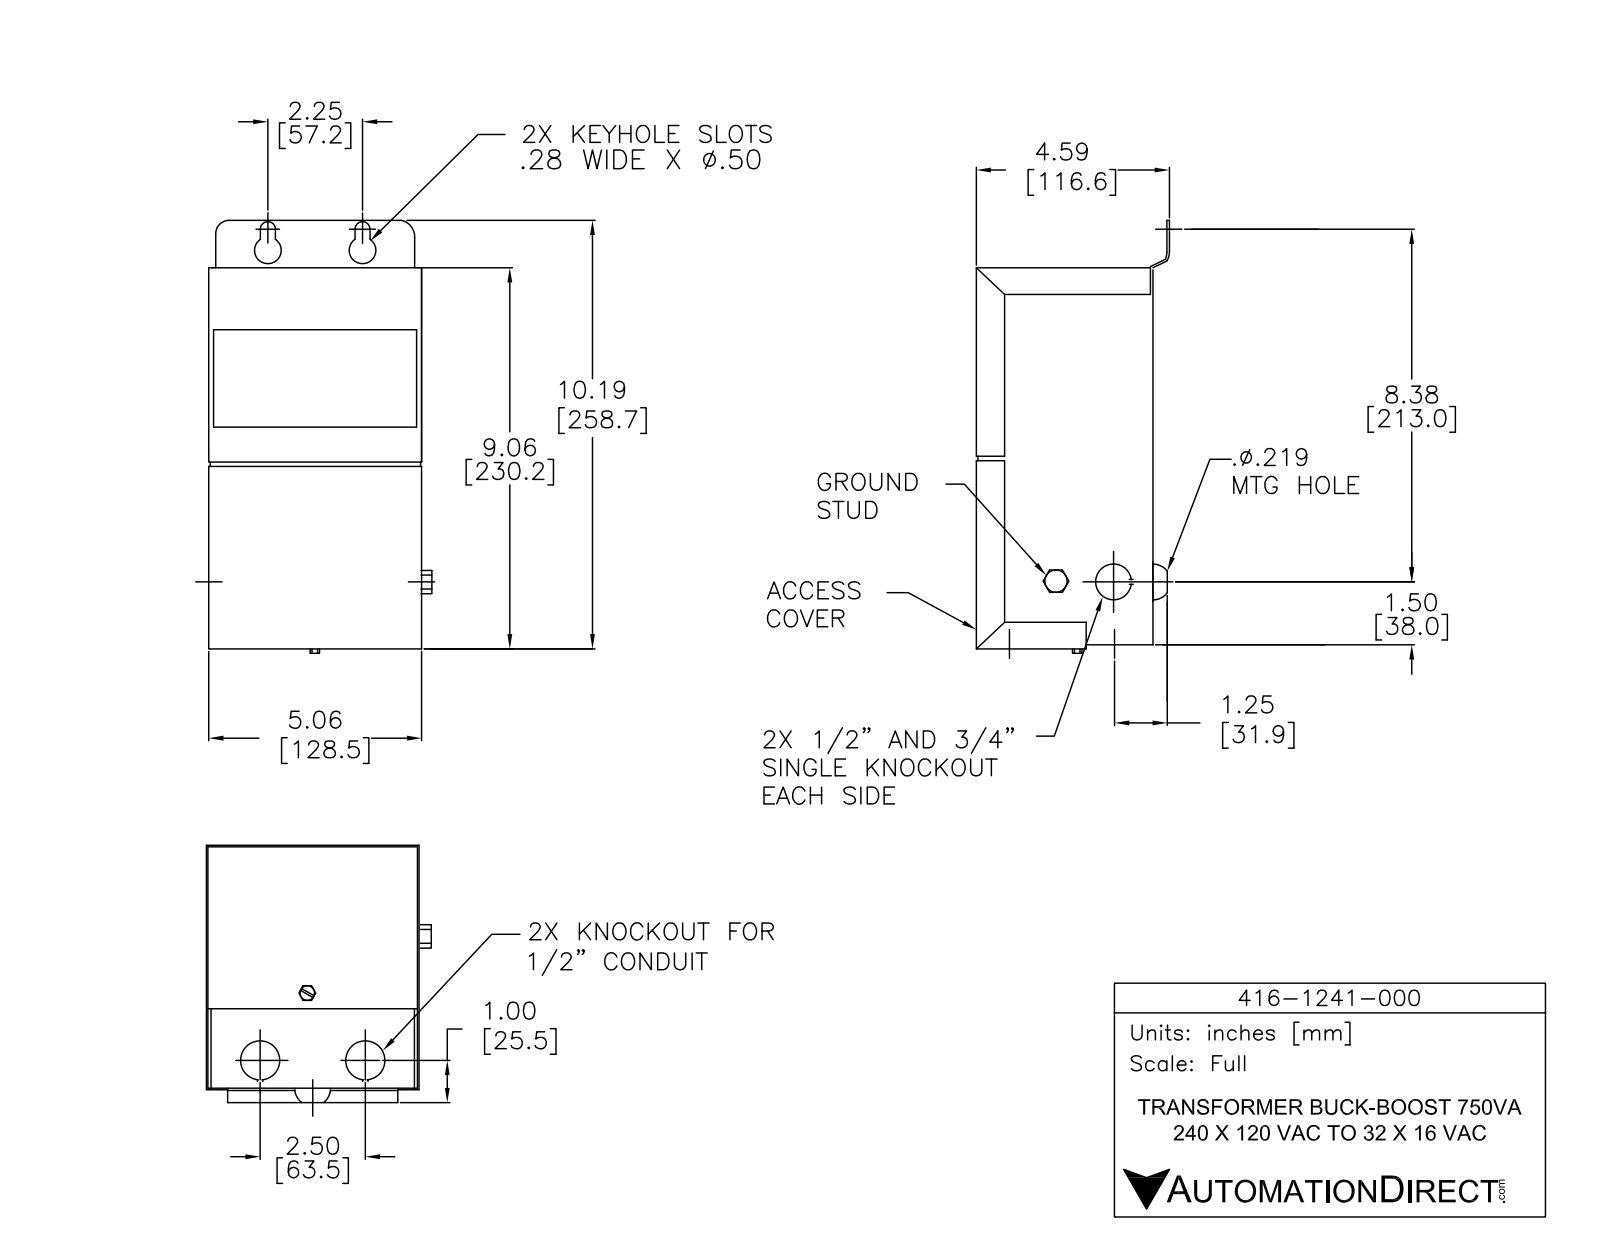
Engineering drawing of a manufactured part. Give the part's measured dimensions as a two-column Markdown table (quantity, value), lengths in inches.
| quantity | value |
| --- | --- |
| part name | 416-1241-000 |
| STEP written by | SolidWorks 2013 (AUTOMOTIVE_DESIGN) |
| units | inches |
| bodies | 1 solid, 159 faces (91 planar, 52 cylindrical, 16 other) |
| overall size | 10.3 × 5.17 × 4.591 |
| volume | 190.3 in³ |
| surface area | 225.3 in² |
| round holes (diameter × count) | 0.5 × 2, 0.875 × 2, 0.219 × 1, 0.232 × 1, 0.29 × 1, 0.875 × 1 |
| round bosses / shafts (diameter × count) | 1.125 × 1 |
| partial cylindrical surfaces (radius × count) | 0.04 × 10, 0.25 × 10, 0.14 × 2, 0.06 × 1, 0.149 × 1, 0.189 × 1 |
| main face-to-face distances | 4.2, 4.98, 0.04, 5.02, 4.201, 9.06, 5.06, 9.02, 0.04, 0.39 |
| hole center spacings | 1.719, 8.168, 1.37, 2.25, 2.5 |
